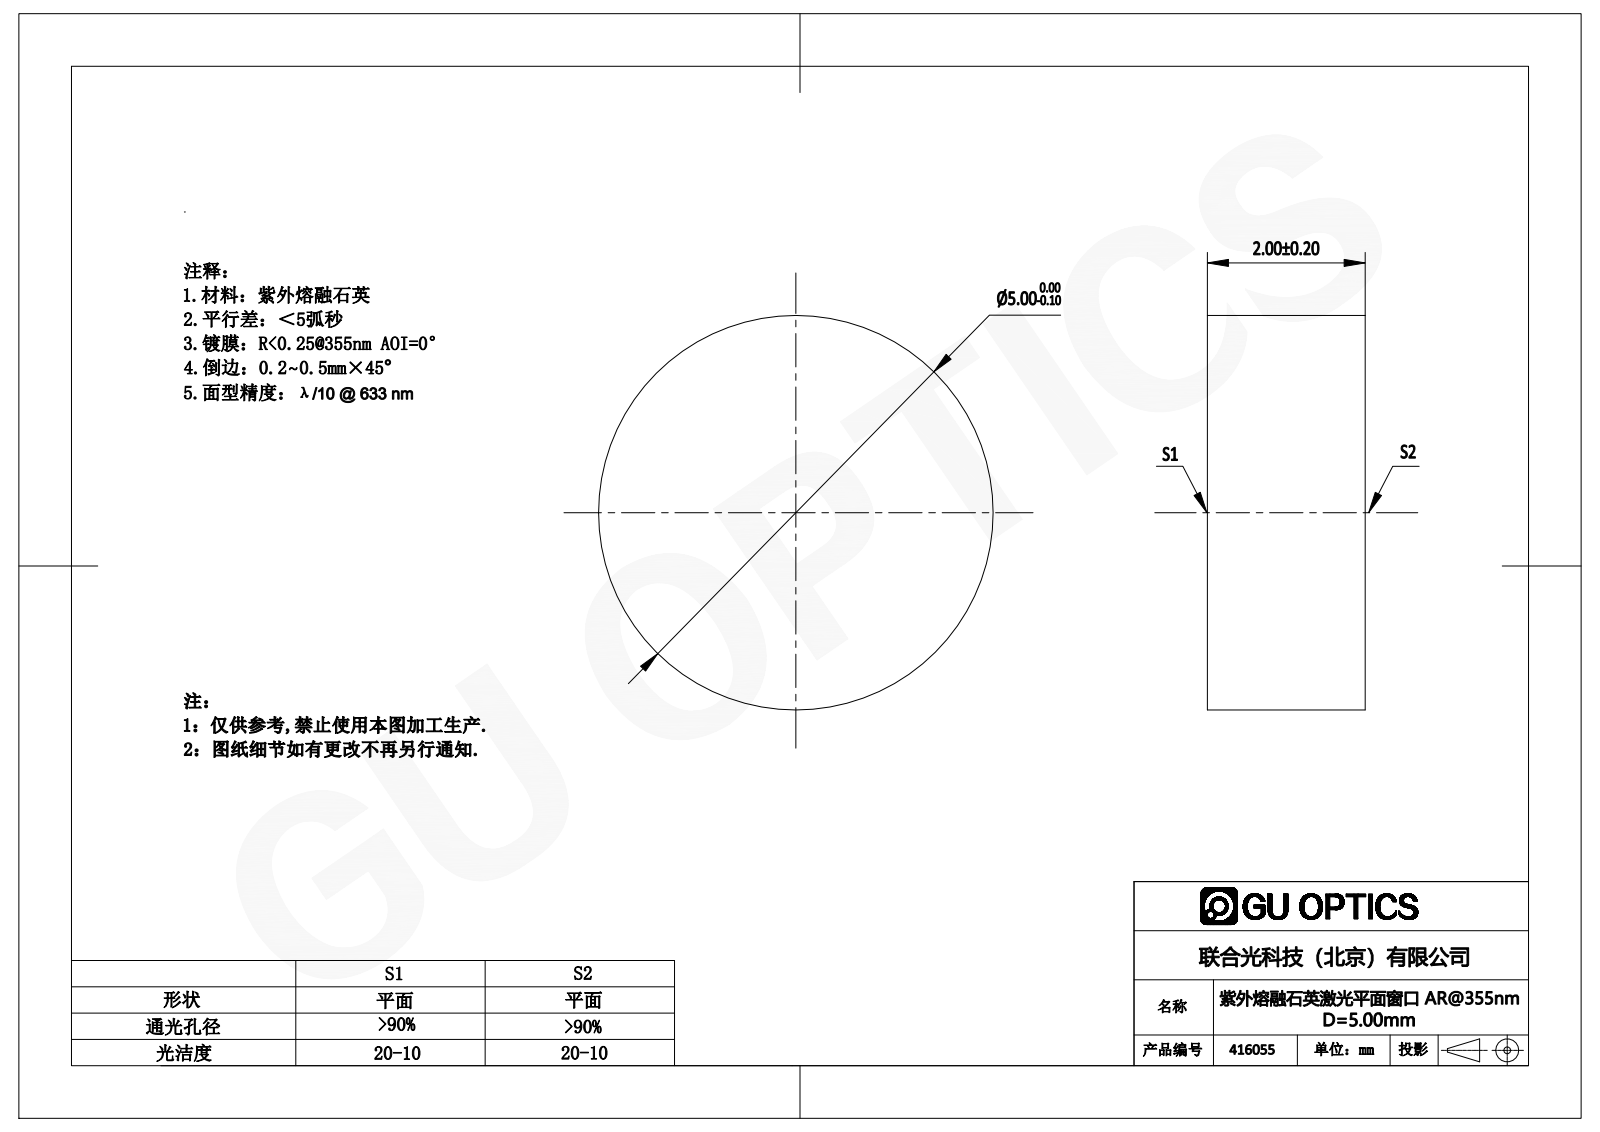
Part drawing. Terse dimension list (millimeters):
name: 416000
written by: SolidWorks 2016 (CONFIG_CONTROL_DESIGN)
unit: mm
bodies: 1 solid, 4 faces (2 planar, 2 cylindrical, 0 other)
size: 5 × 5 × 2
volume: 39 mm³; area: 71 mm²
bosses: 1× ⌀5
face distances: 2
